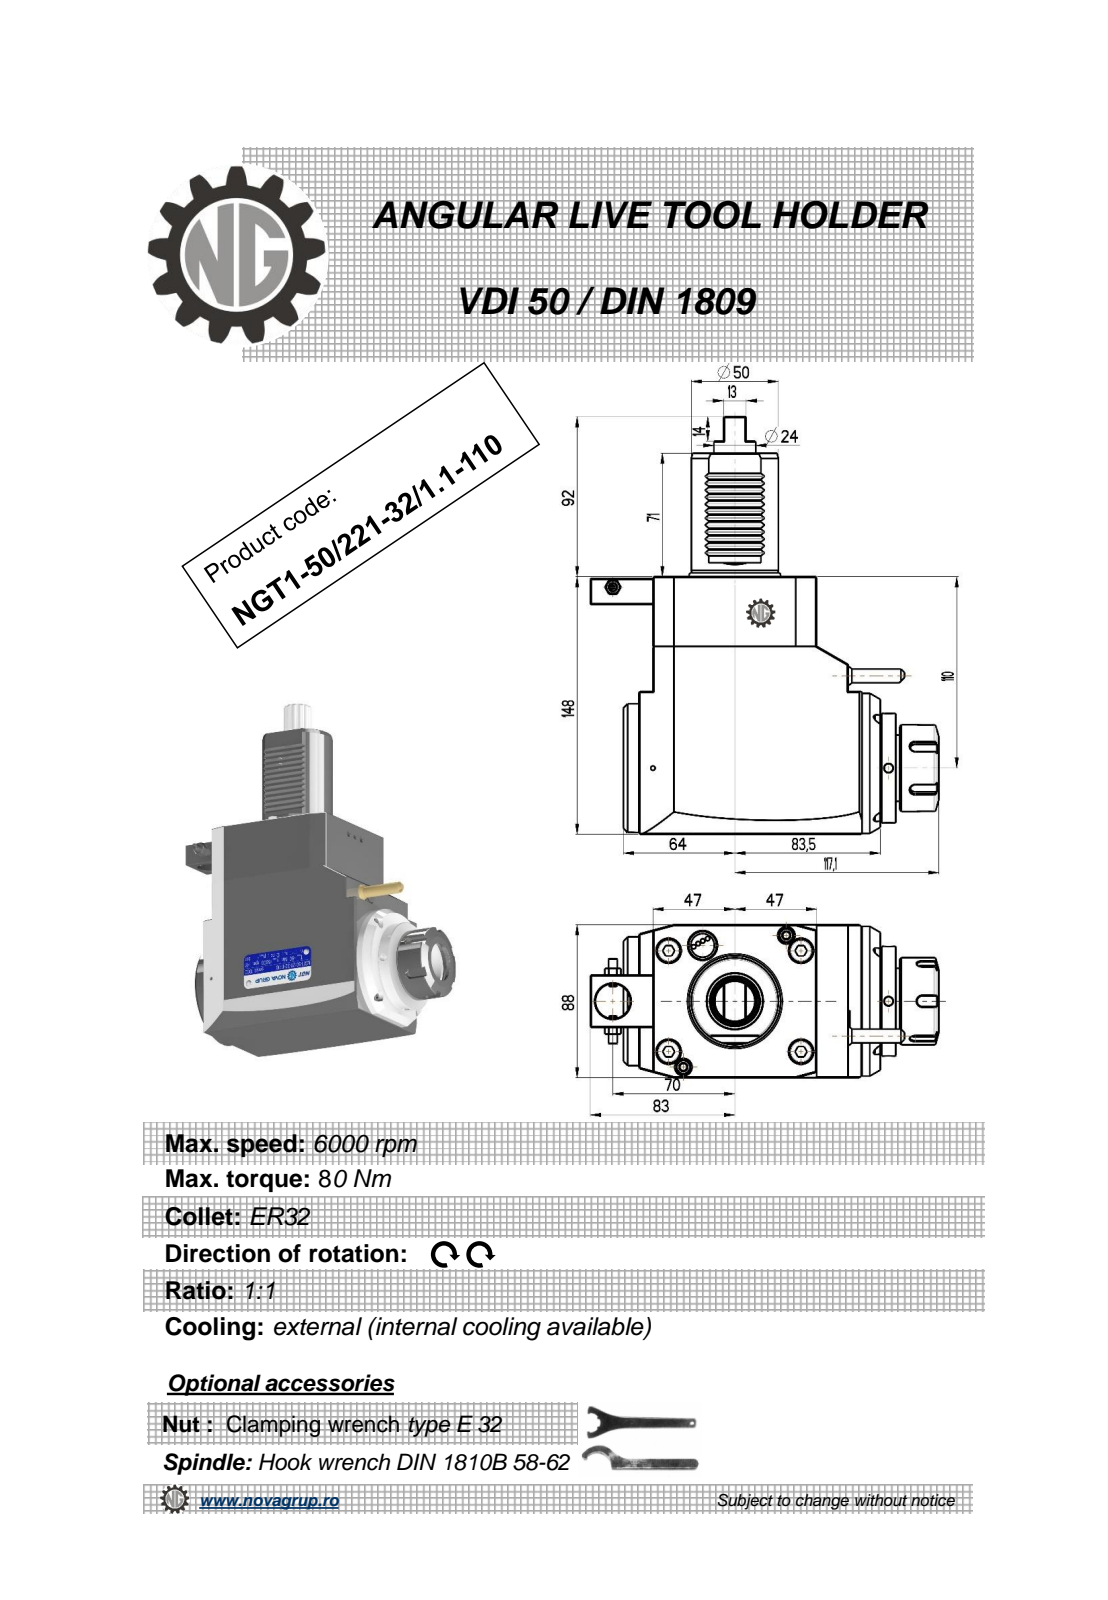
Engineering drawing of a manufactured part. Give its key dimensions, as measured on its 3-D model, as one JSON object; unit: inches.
{"part_name": "NGT1_50_221_32_1_1_110", "step_written_by": "PRO/ENGINEER BY PARAMETRIC TECHNOLOGY CORPORATION, 2010280 (CONFIG_CONTROL_DESIGN)", "units": "inches", "bodies": {"solids": 1, "faces": 397, "planar": 194, "cylindrical": 87, "other": 116}, "overall_size": [9.449, 7.878, 3.465], "volume_in3": 110, "surface_area_in2": 173.5, "round_holes": [[0.197, 3], [0.118, 1], [0.374, 1], [0.787, 1], [1.063, 1]], "round_bosses_or_shafts": [[1.969, 2], [3.386, 1], [2.913, 1], [2.48, 1], [1.988, 1], [1.614, 1], [0.945, 1], [0.394, 1]], "partial_cylinders_radius": [[0.01, 12], [0.012, 12], [0.008, 6], [0.118, 5], [0.031, 2], [0.098, 1]], "face_to_face_distances": [3.465, 5.827, 5.807, 0.354, 0.669, 0.315, 3.701, 4.37, 5.138, 1.437], "hole_center_spacings": [2.065, 2.23, 3.996, 6.23]}
